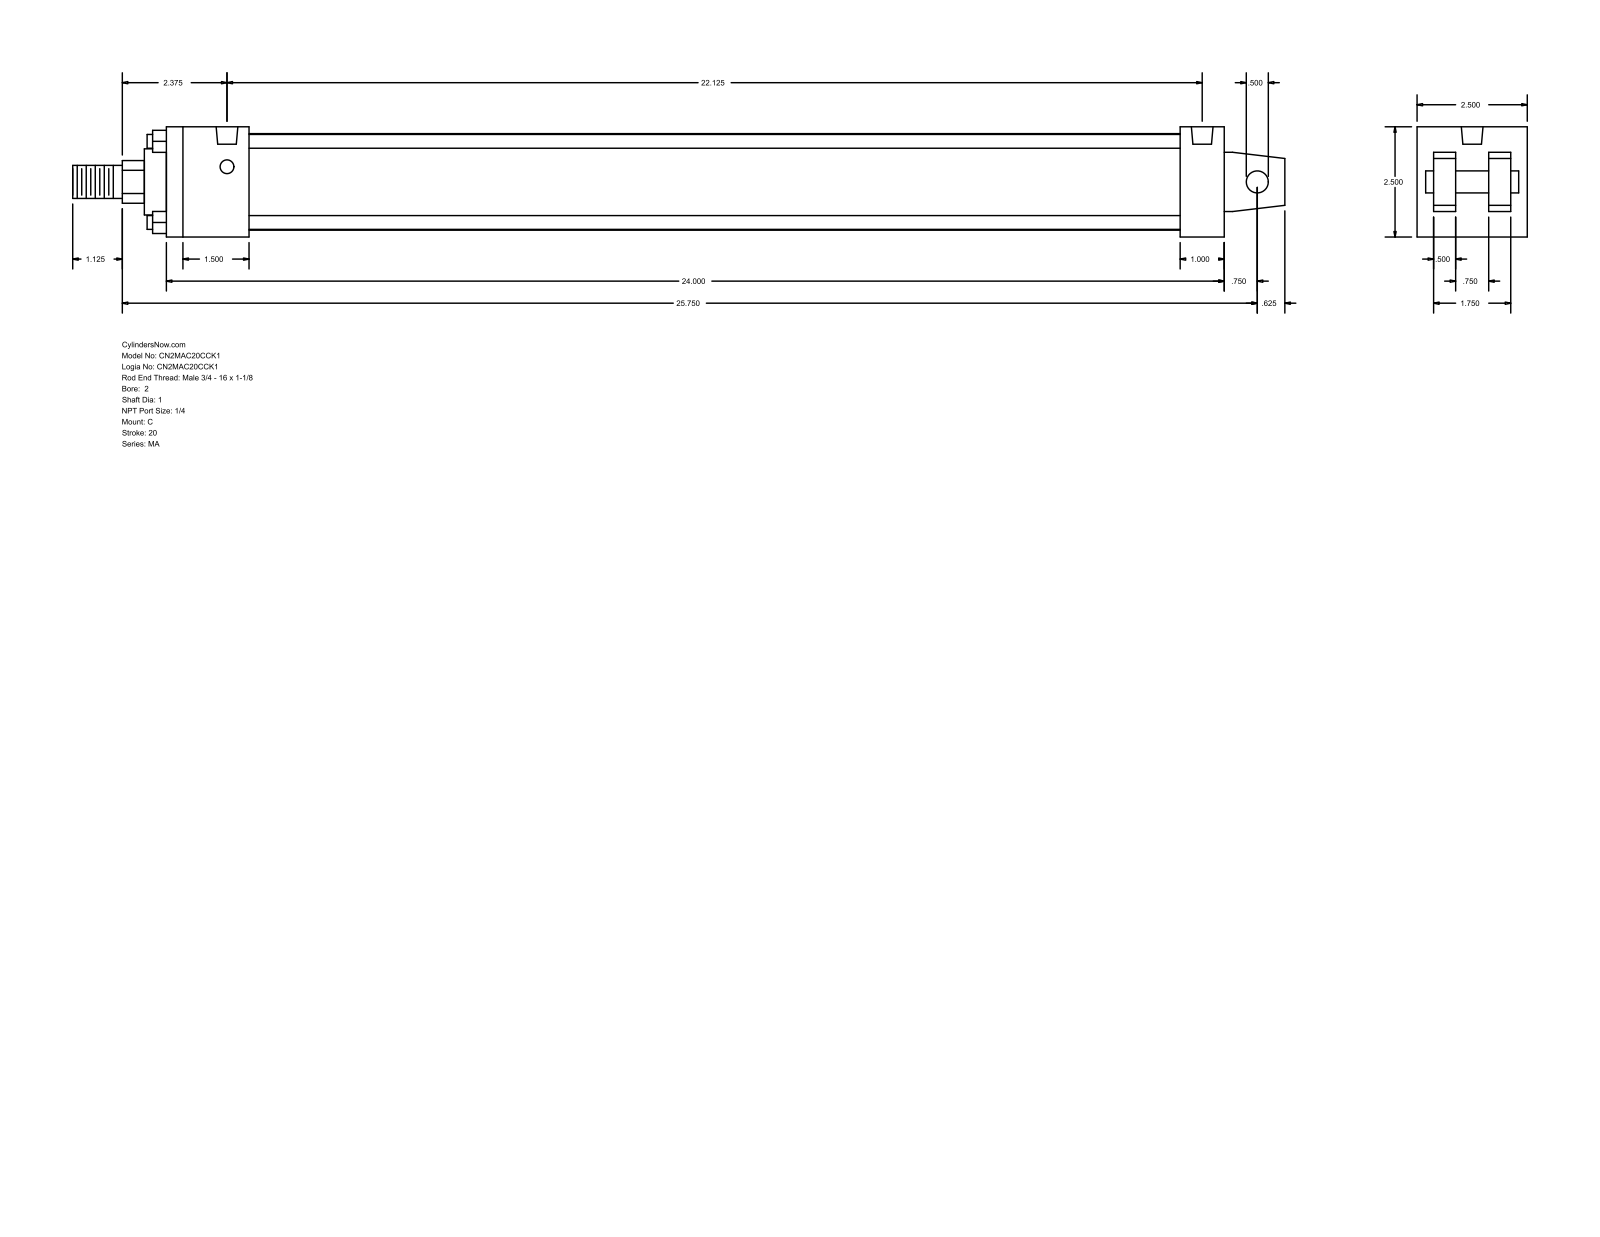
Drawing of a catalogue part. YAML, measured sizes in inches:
part_name: "MA_C__0200_1"
step_written_by: "GSSL Pune (CONFIG_CONTROL_DESIGN)"
units: inches
bodies: {solids: 0, faces: 103, planar: 76, cylindrical: 27, other: 0}
overall_size: [27.5, 2.5, 2.5]
round_holes:
  - {diameter: 0.313, count: 4}
  - {diameter: 0.492, count: 2}
round_bosses_or_shafts:
  - {diameter: 0.313, count: 4}
  - {diameter: 2.19, count: 1}
  - {diameter: 1.5, count: 1}
  - {diameter: 1, count: 1}
  - {diameter: 0.75, count: 1}
  - {diameter: 0.5, count: 1}
partial_cylinders:
  - {radius: 0.484, count: 1}
face_to_face_distances: [2.5, 0.5, 24, 0.875, 1.625, 0.375, 2.125, 1.25, 1.875, 1]
hole_center_spacings: [22.125]
